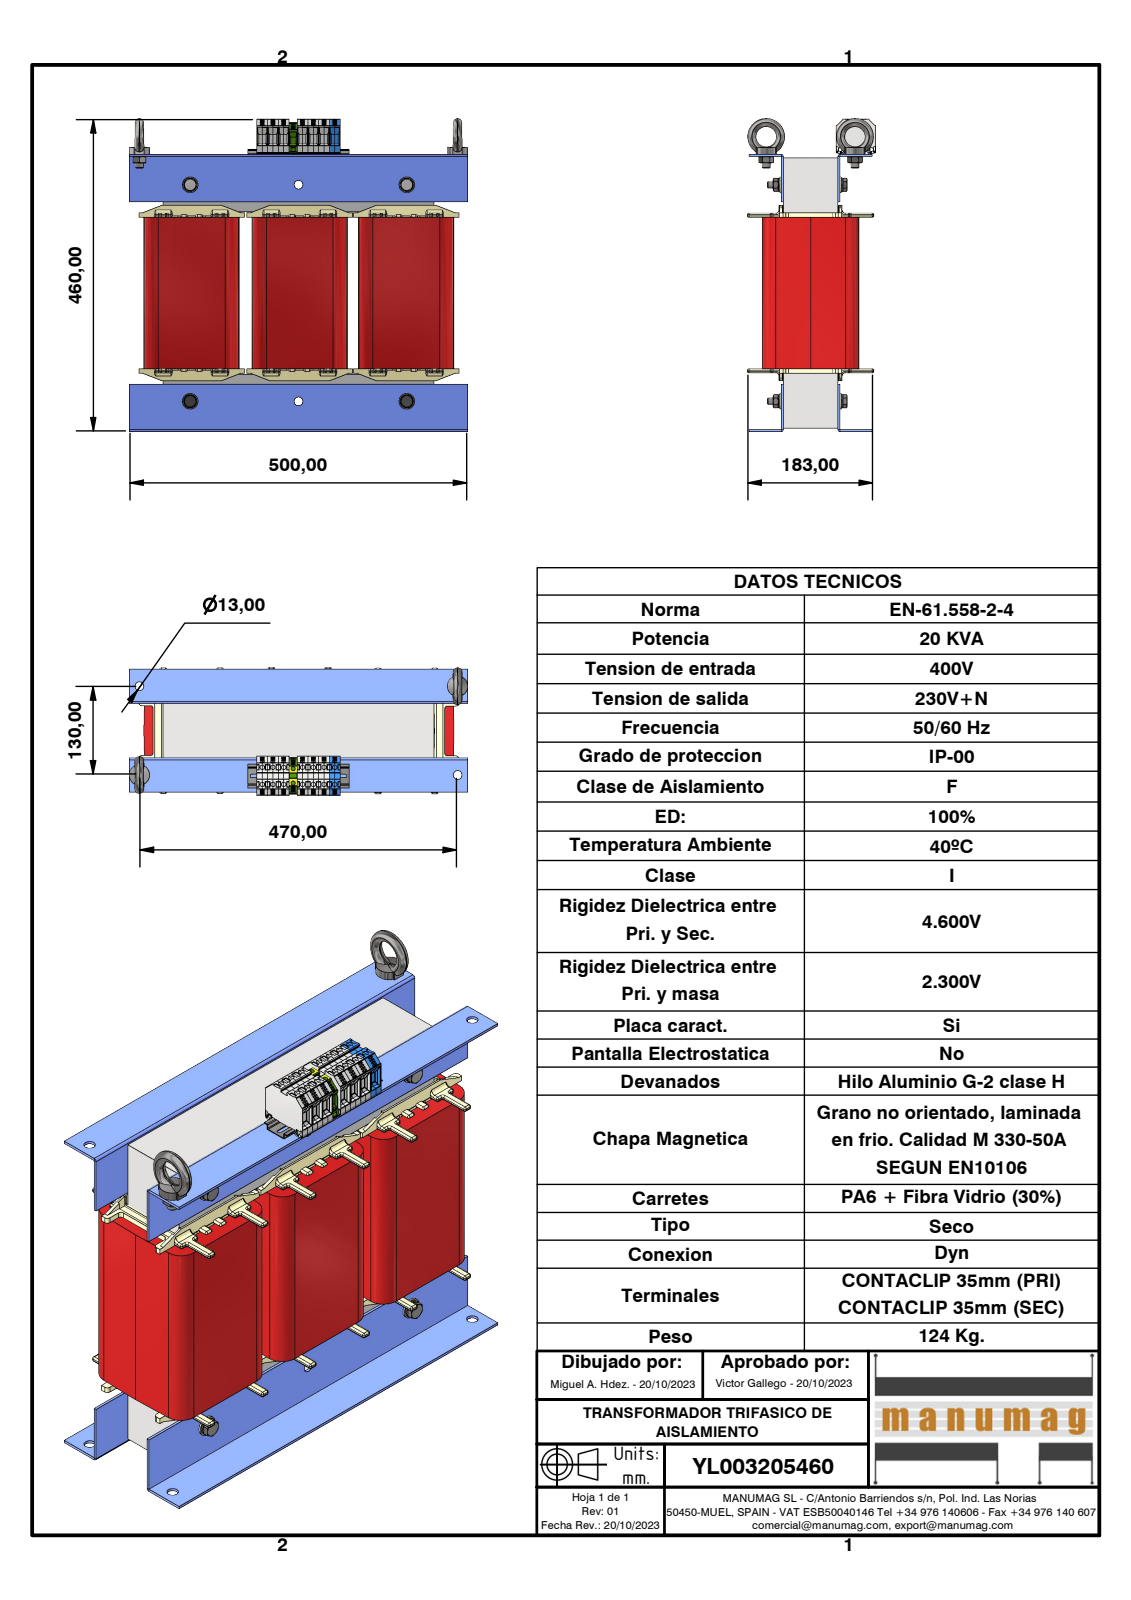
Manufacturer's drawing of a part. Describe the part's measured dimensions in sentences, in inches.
The part is named "YL003205460; 3UI240 400 x 400 - 80; RC80 NT080; centrador M10 (+8 more)". Its 3-D file was written by "Autodesk Inventor 2023 (AUTOMOTIVE_DESIGN)". It is 45 solids with 8809 faces: 4833 planar, 2622 cylindrical and 1354 other. Overall it measures 19.685 by 18.228 by 7.398 inches. Its volume is 1 154 cubic inches and its surface area 3 683 square inches. Round holes: 14 of diameter 0.256, 10 of diameter 0.512, 6 of diameter 0.591, 4 of diameter 0.079, 4 of diameter 0.33, 4 of diameter 0.394, 4 of diameter 0.413, 2 of diameter 0.248, 2 of diameter 0.398, 2 of diameter 1.181. Round bosses or shafts: 12 of diameter 0.024, 4 of diameter 0.906, 4 of diameter 0.787, 4 of diameter 0.606, 4 of diameter 0.453, 4 of diameter 0.362, 2 of diameter 2.126, 2 of diameter 0.472. Partial cylindrical surfaces (rounded edges, fillets, slot ends): 494 of radius 0.012, 218 of radius 0.079, 188 of radius 0.02, 94 of radius 0.039, 36 of radius 0.075, 34 of radius 0.01, 33 of radius 0.032, 28 of radius 0.197. The main face-to-face distances are 3.15, 0.118, 0.228, 3.524, 0.904, 3.268, 0.02, 4.428, 0.197, 0.028. The hole center spacings are 0.626, 1.167, 0.984, 1.252, 1.593, 2.346, 2.544, 2.972.
